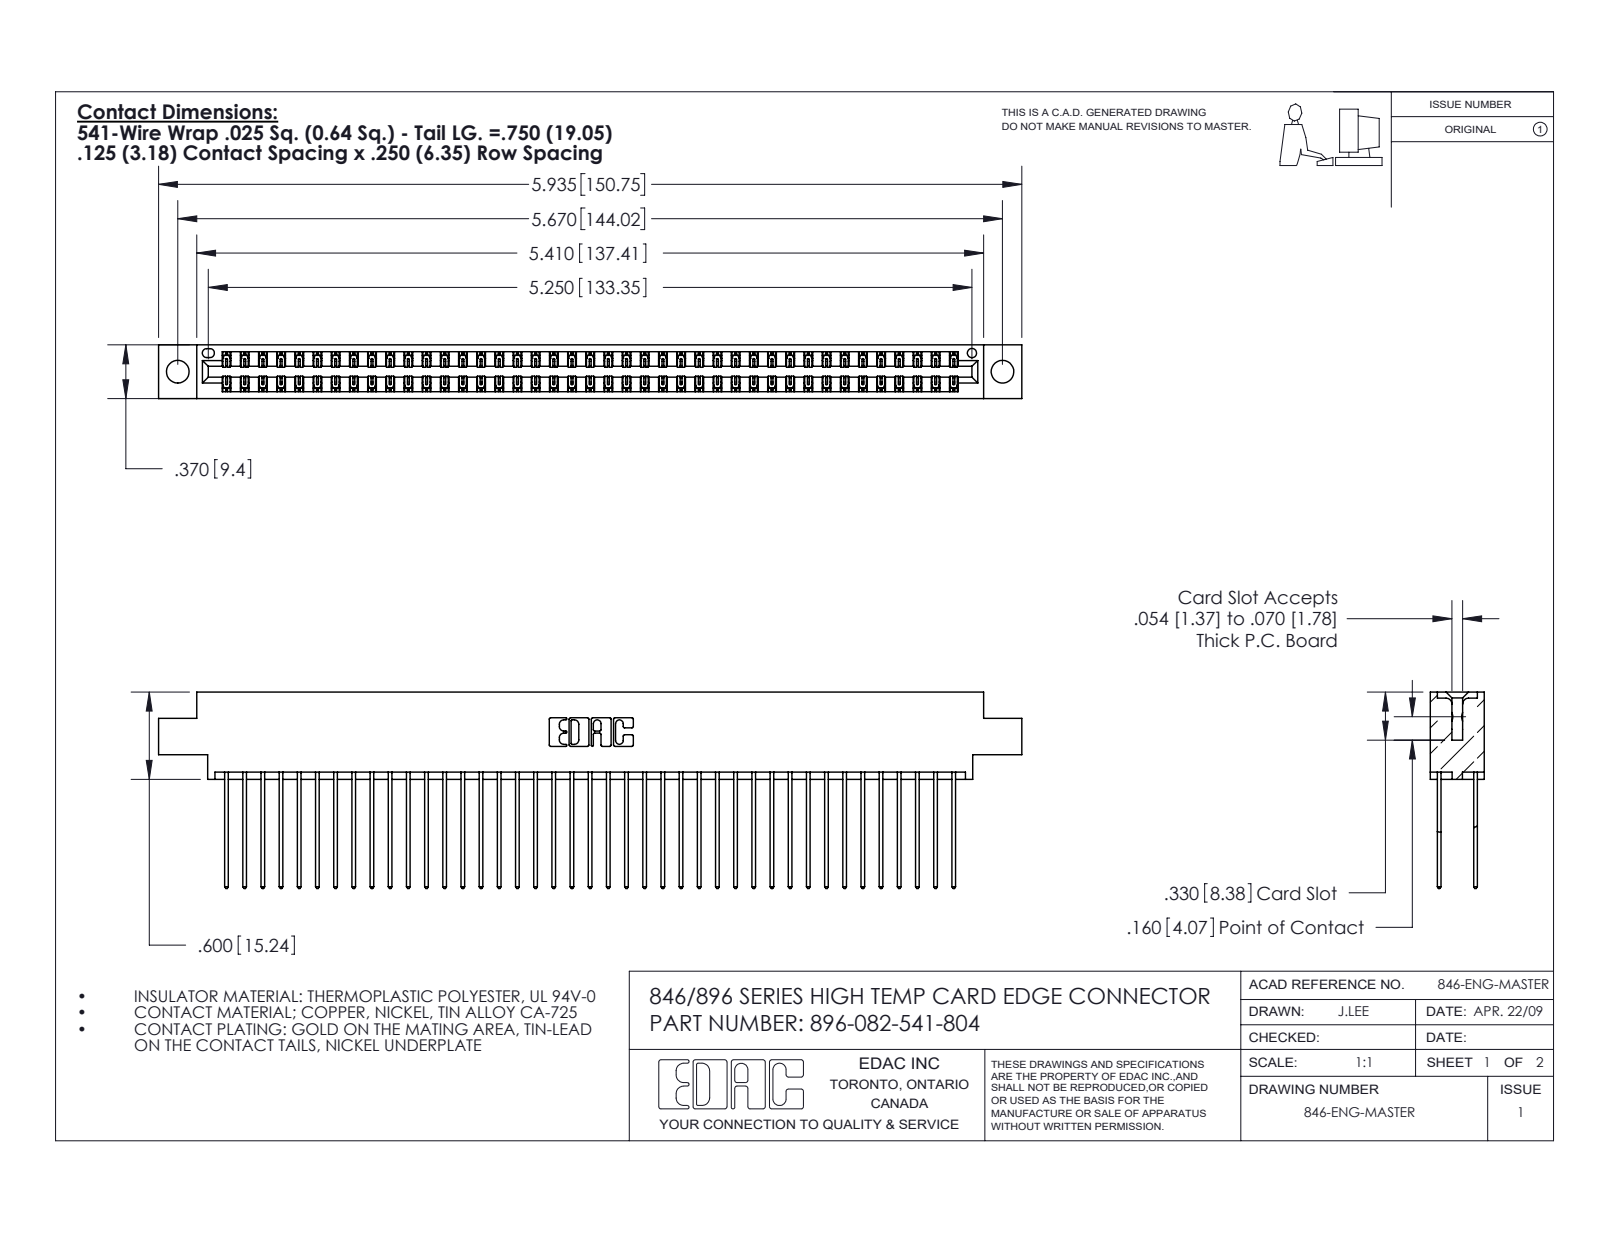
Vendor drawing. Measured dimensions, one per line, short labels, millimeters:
name: 345-292-001_345-293-141; 396-082-541-804; 346 Part_0.170 Offset - 0.156 Dia-TH
written by: SolidWorks 2016 (CONFIG_CONTROL_DESIGN)
unit: mm
bodies: 83 solids, 4390 faces (2950 planar, 1440 cylindrical, 0 other)
size: 150.7 × 34.3 × 9.4
volume: 14 900 mm³; area: 22 740 mm²
holes: 2× ⌀4, 1× ⌀1.6
rounds: 123× R0.2, 82× R0.3, 22× R0.3, 6× R0.2, 6× R0.8, 3× R0.7, 2× R0.4, 2× R0.6
face distances: 1.2, 8.2, 6.4, 1.8, 7.6, 0.6, 9.4, 7, 5.7, 3.8
hole spacings: 6.2, 138.7, 144
